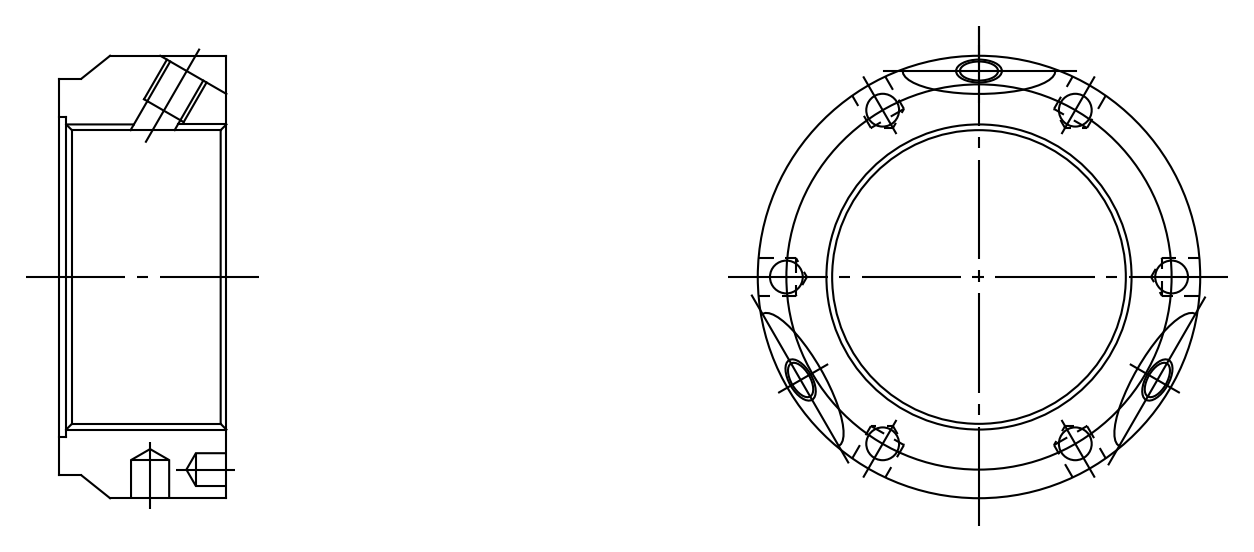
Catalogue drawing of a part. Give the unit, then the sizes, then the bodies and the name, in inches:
Units: inches
Overall size (bounding box): 2.283 × 2.283 × 0.866
Round holes (diameter × count): ⌀0.169 ×6, ⌀0.197 ×3, ⌀0.24 ×3, ⌀0.194 ×2, ⌀0.194 ×1, ⌀1.575 ×1, ⌀1.654 ×1
Round bosses / shafts (diameter × count): ⌀2.283 ×1, ⌀2.047 ×1
Partial cylindrical surfaces — rounded edges, fillets, slot ends (radius × count): R0.787 ×3
Main face-to-face distances: 0.866, 0.059, 0.807
Hole centre spacings: 0.994, 1.722, 0.994, 1.989, 1.988
Volume: 1.663 in³ · Surface area: 16.31 in²
Bodies: 1 solid, 44 faces (6 planar, 25 cylindrical, 13 other)
Part name (STEP PRODUCT): FKD FKNA40
STEP written by: Autodesk Inventor LT (CONFIG_CONTROL_DESIGN)
